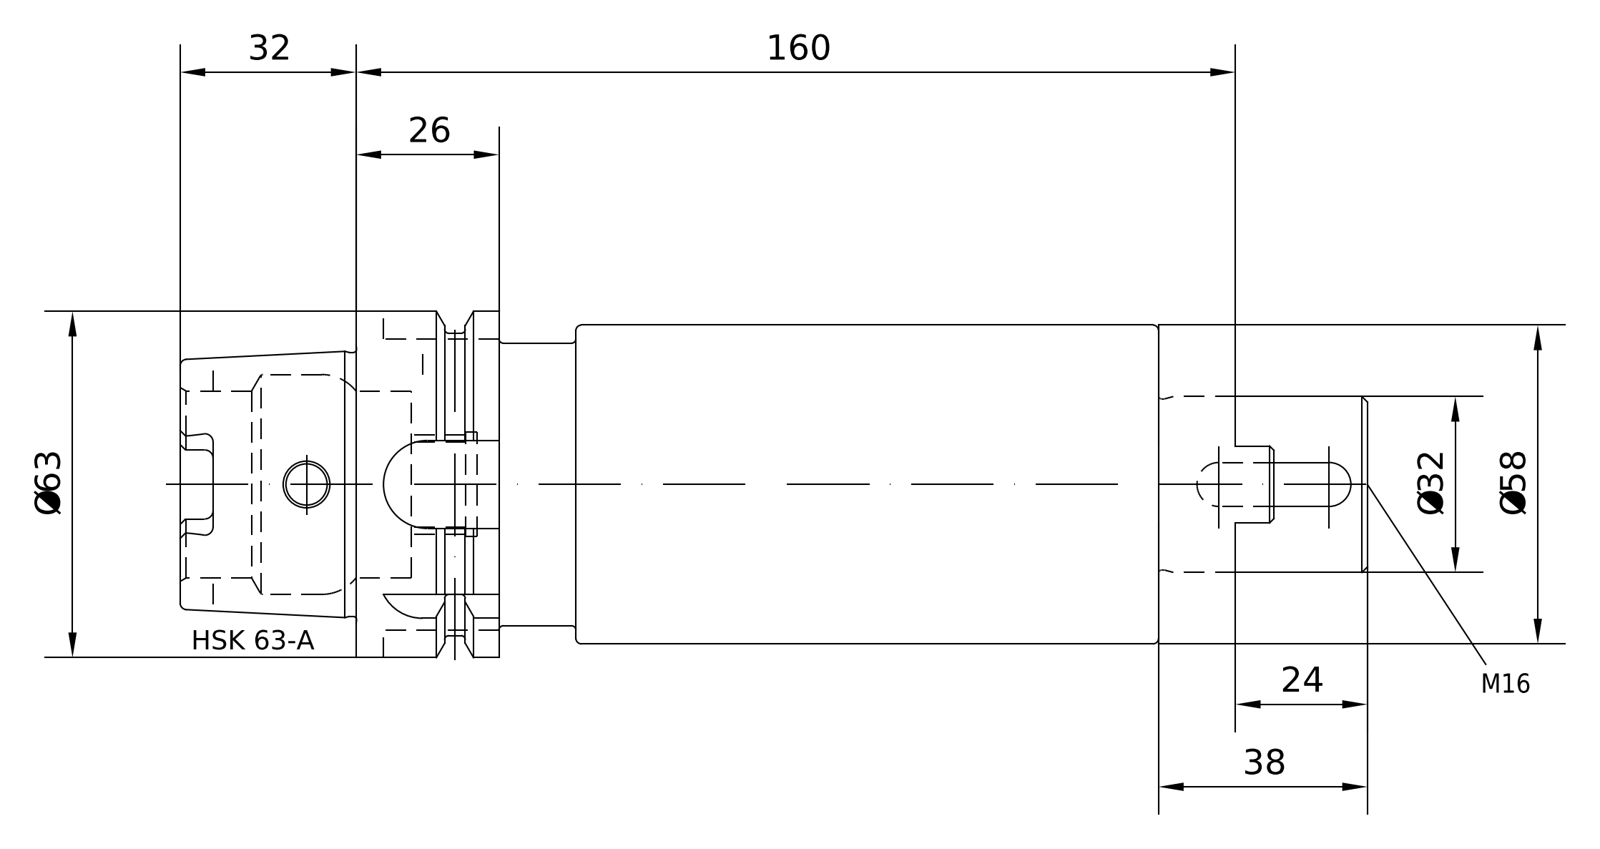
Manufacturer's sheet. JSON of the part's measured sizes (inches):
{"part_name": "A63-042-32; 85-200-32; A63-042-32_ASM", "step_written_by": "PRO/ENGINEER BY PARAMETRIC TECHNOLOGY CORPORATION, 2010430 (CONFIG_CONTROL_DESIGN)", "units": "inches", "bodies": {"solids": 2, "faces": 273, "planar": 125, "cylindrical": 66, "other": 82}, "overall_size": [8.504, 2.48, 2.48], "volume_in3": 26.58, "surface_area_in2": 96.15, "round_holes": [[0.295, 1], [0.394, 1], [0.551, 1], [0.63, 1], [0.666, 1], [0.721, 1], [0.735, 1], [1.275, 1], [1.339, 1], [1.457, 1], [1.575, 1]], "round_bosses_or_shafts": [[2.48, 1], [2.283, 1], [2.165, 1], [2.008, 1], [1.891, 1], [1.26, 1], [0.709, 1]], "partial_cylinders_radius": [[0.059, 6], [0.118, 4], [0.157, 2], [0.278, 1], [0.315, 1], [0.316, 1], [0.355, 1]], "face_to_face_distances": [0.551, 5.748, 6.299, 1.024, 4.724, 5.276, 0.394, 7.244, 6.22, 1.496]}
